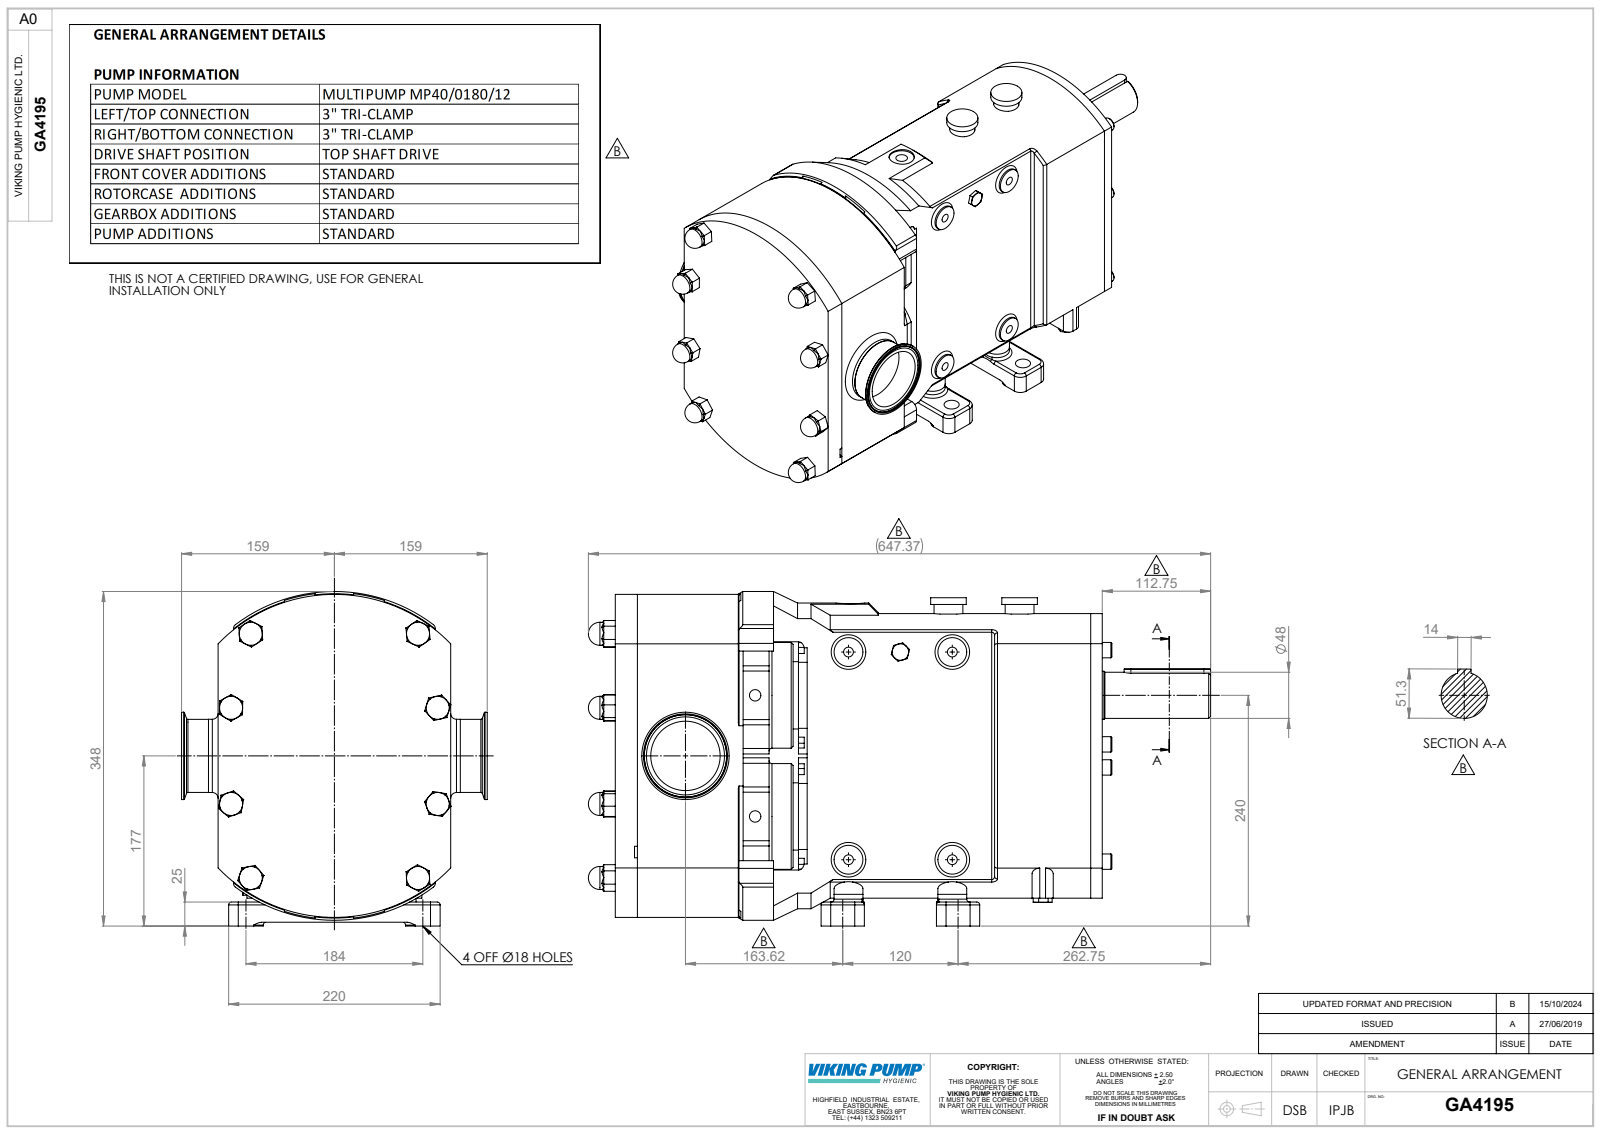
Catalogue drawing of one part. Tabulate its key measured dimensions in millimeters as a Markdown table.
| quantity | value |
| --- | --- |
| part name | Copy of Z94-5121-55 - 3 INCH^GA4195; GA4195; Copy of CP40S-0180 H TSD^GA4195 |
| STEP written by | SolidWorks 2023 (AUTOMOTIVE_DESIGN) |
| units | millimeters |
| bodies | 3 solids, 957 faces (365 planar, 271 cylindrical, 321 other) |
| overall size | 647.37 × 348 × 318 |
| volume | 26 270 000 mm³ |
| surface area | 901 922 mm² |
| round holes (diameter × count) | 10.2 × 4, 18 × 4, 11.89 × 2, 35 × 2, 13.83 × 1, 30 × 1, 72.2 × 1 |
| round bosses / shafts (diameter × count) | 30 × 10, 24 × 8, 16 × 6, 110 × 2, 70 × 2, 37 × 2, 31.75 × 2, 250 × 1 |
| partial cylindrical surfaces (radius × count) | 10 × 24, 3 × 22, 8 × 20, 6 × 10, 5 × 4, 11 × 4, 7 × 2, 13 × 2 |
| main face-to-face distances | 21, 30, 161, 51, 191, 212, 140, 506.62, 182, 242 |
| hole center spacings | 92.35, 92.54, 96.05, 107.04, 108, 112.07, 120, 143.4 |
